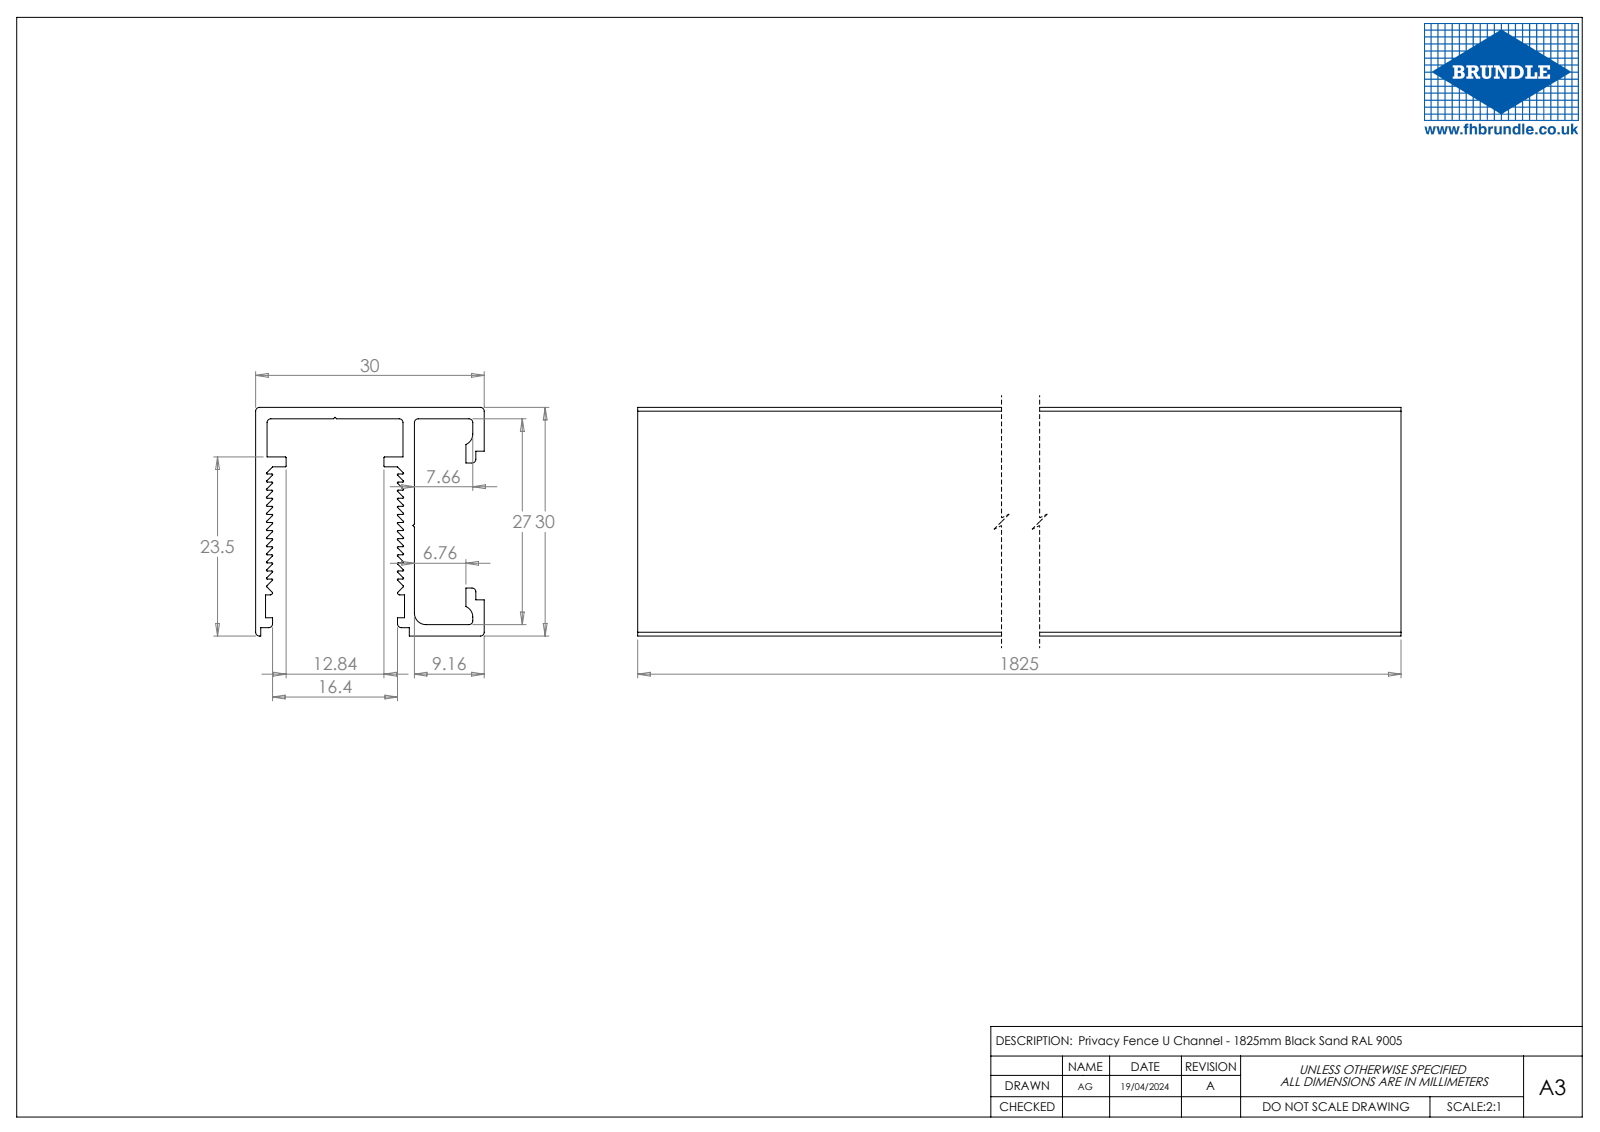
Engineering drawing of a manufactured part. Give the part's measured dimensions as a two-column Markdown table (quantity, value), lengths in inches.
| quantity | value |
| --- | --- |
| part name | 76PFCSBS; 76PFCK16BS; 76PFPTBS; 76PFUC16BS |
| STEP written by | SolidWorks 2023 (CONFIG_CONTROL_DESIGN) |
| units | inches |
| bodies | 3 solids, 281 faces (153 planar, 128 cylindrical, 0 other) |
| overall size | 71.969 × 1.181 × 1.181 |
| volume | 23.88 in³ |
| surface area | 956.6 in² |
| partial cylindrical surfaces (radius × count) | 0.02 × 23, 0.004 × 10, 0.059 × 6, 0.012 × 2 |
| main face-to-face distances | 0.059, 0.82, 0.03, 1.122, 1.179, 0.358, 0.089, 1.181, 0.118, 0.319 |
